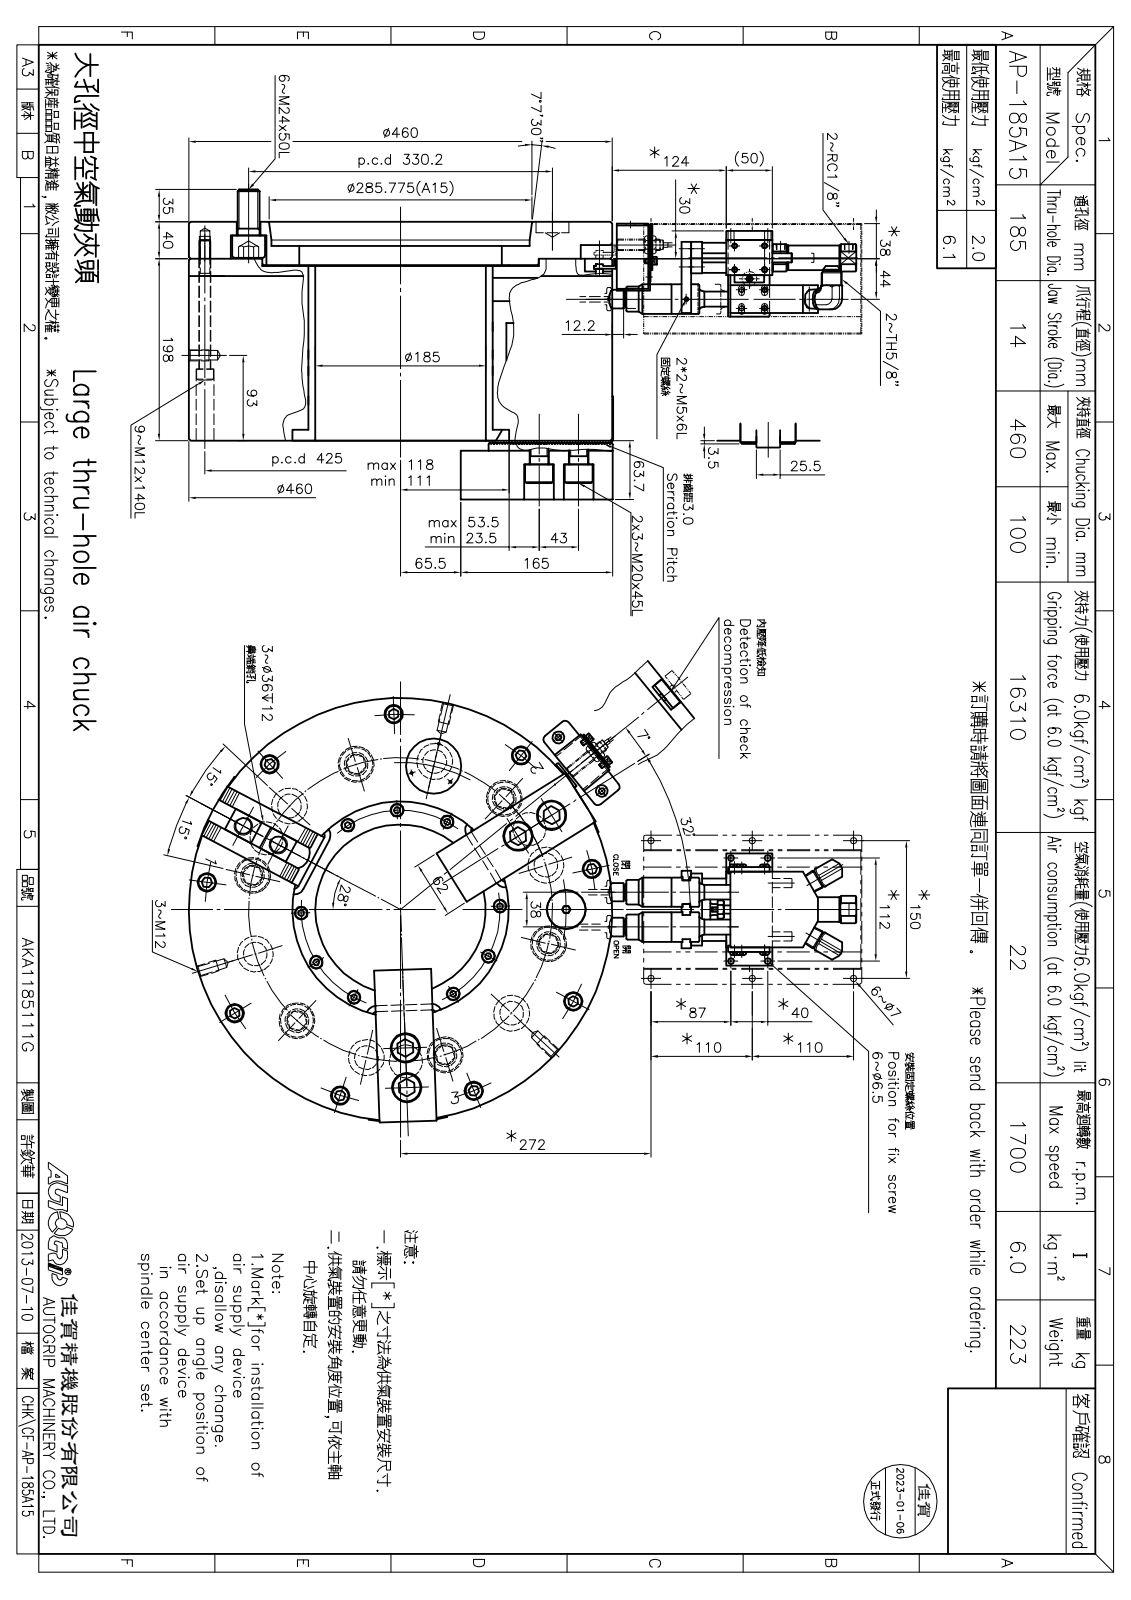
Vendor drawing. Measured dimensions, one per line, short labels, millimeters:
name: CF-AP-185-0101G; 圓頭內六角螺栓_M12x140; CF-AP-185-08000; CF-AP-145-15000 (+8 more)
written by: SolidWorks 2016 (CONFIG_CONTROL_DESIGN)
unit: mm
bodies: 45 solids, 2971 faces (1686 planar, 906 cylindrical, 379 other)
size: 461.89 × 460 × 301.7
volume: 24 580 000 mm³; area: 2 161 000 mm²
holes: 22× ⌀13, 17× ⌀20, 13× ⌀10.2, 12× ⌀26, 12× ⌀39, 10× ⌀14, 9× ⌀9, 9× ⌀19, 7× ⌀6.8, 6× ⌀6, 6× ⌀15, 6× ⌀21
bosses: 19× ⌀18, 18× ⌀12, 9× ⌀13, 6× ⌀30, 6× ⌀20, 6× ⌀8, 2× ⌀16, 2× ⌀14.8
rounds: 168× R0.2, 1× R20
face distances: 198, 179, 40, 238, 28, 170, 21, 19, 59, 68
hole spacings: 212.5, 273.18, 216, 145.36, 175, 368.06, 418.54, 50.36
